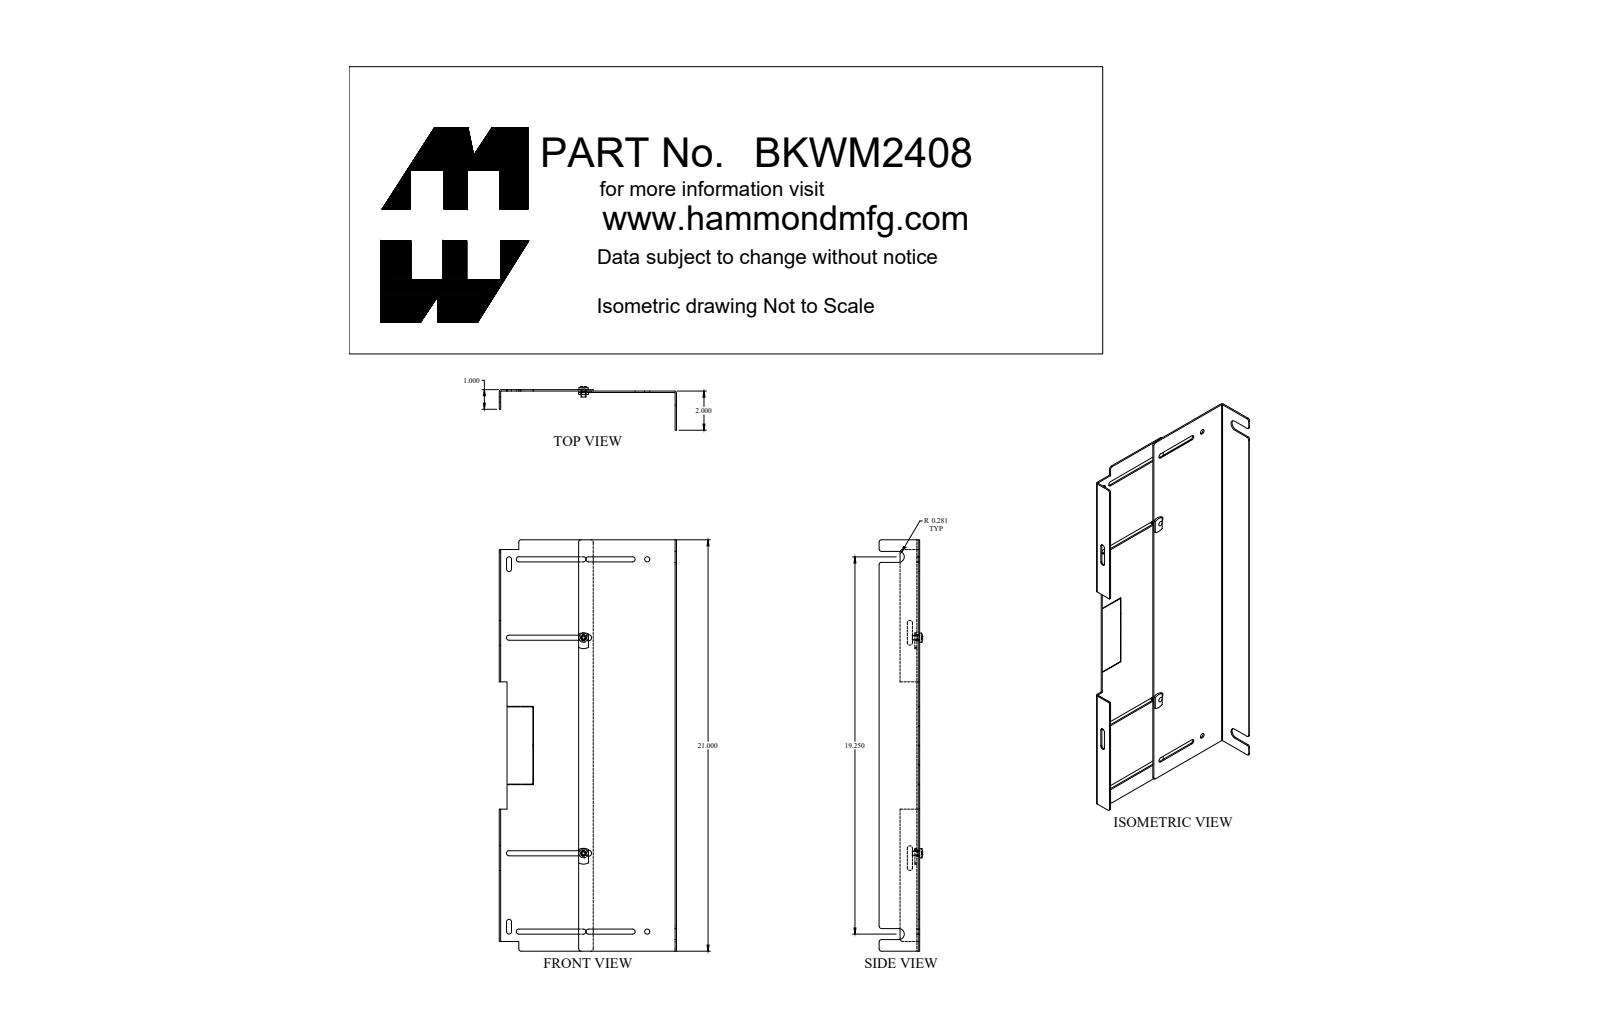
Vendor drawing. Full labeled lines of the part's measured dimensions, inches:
Part name (STEP PRODUCT): BKWM2408_Default
STEP written by: SolidWorks 2019 (CONFIG_CONTROL_DESIGN)
Units: inches
Bodies: 6 solids, 216 faces (116 planar, 78 cylindrical, 22 other)
Overall size (bounding box): 21 × 9.055 × 2.237
Volume: 17.87 in³ · Surface area: 509.3 in²
Round holes (diameter × count): ⌀0.201 ×2, ⌀0.26 ×2, ⌀0.313 ×2
Round bosses / shafts (diameter × count): ⌀0.468 ×2, ⌀0.293 ×2, ⌀0.25 ×2
Partial cylindrical surfaces — rounded edges, fillets, slot ends (radius × count): R0.125 ×18, R0.13 ×16, R0.5 ×4, R0.036 ×2, R0.108 ×2, R0.281 ×2
Main face-to-face distances: 0.072, 0.144, 8.983, 9.055, 8.911, 4.8, 4.728, 4.183, 4.255, 4.055
Hole centre spacings: 5, 15.297, 11, 19
